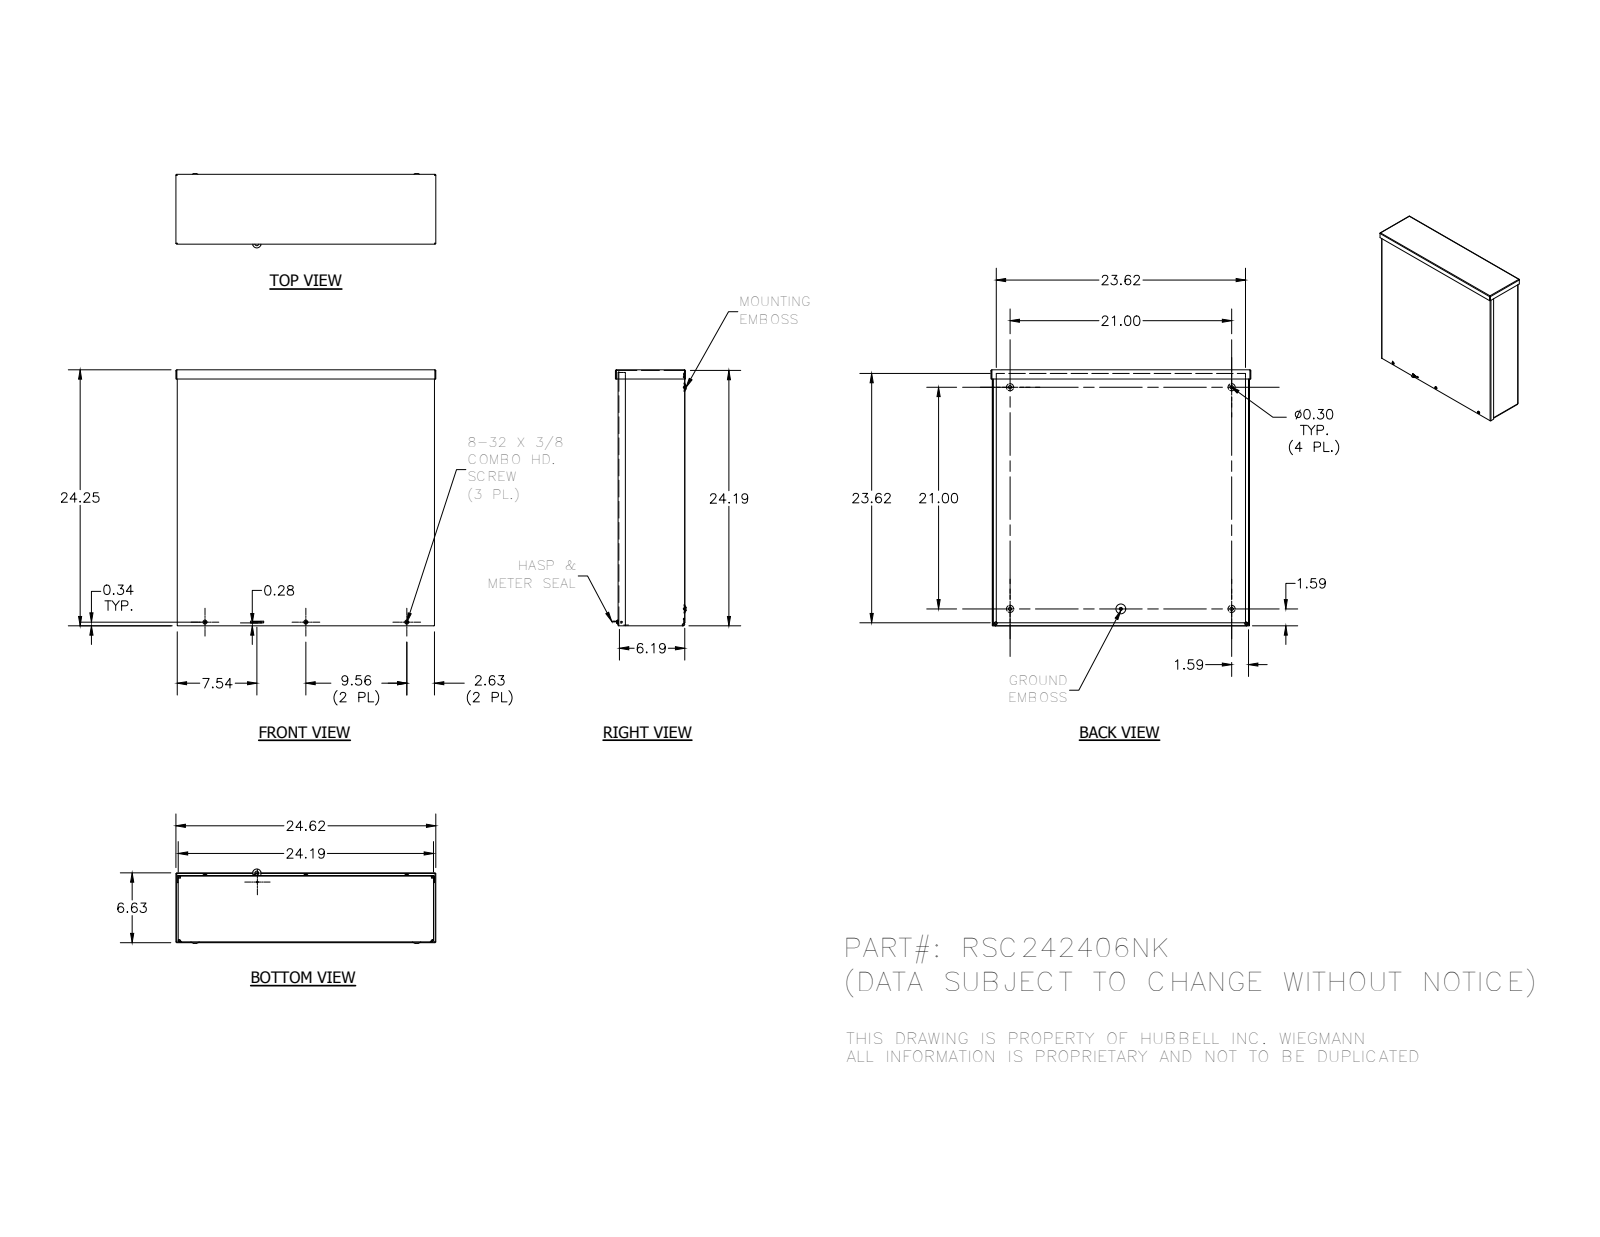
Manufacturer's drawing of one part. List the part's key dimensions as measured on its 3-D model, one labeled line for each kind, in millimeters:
Part name (STEP PRODUCT): RSC242406NK_WRAP; RSC2424NK_LID; RSC2406NK_CAP; 3183 (+3 more)
STEP written by: Autodesk Inventor 2014 (AUTOMOTIVE_DESIGN)
Units: millimetres
Bodies: 8 solids, 407 faces (173 planar, 83 cylindrical, 151 other)
Overall size (bounding box): 625.48 × 615.96 × 180.97
Volume: 2 158 000 mm³ · Surface area: 2 755 000 mm²
Round holes (diameter × count): ⌀7.95 ×6, ⌀7.62 ×4, ⌀3.76 ×3, ⌀3.17 ×1, ⌀3.45 ×1, ⌀3.96 ×1, ⌀4.19 ×1, ⌀9.52 ×1
Round bosses / shafts (diameter × count): ⌀9.75 ×3, ⌀4.17 ×3, ⌀5.8 ×1
Partial cylindrical surfaces — rounded edges, fillets, slot ends (radius × count): R0.79 ×8, R2.37 ×8, R3.17 ×8, R4.75 ×8, R1.4 ×4, R1.57 ×4, R2.38 ×4, R2.97 ×4
Main face-to-face distances: 1.58, 158.73, 157.15, 612.79, 1.59, 160.32, 158.74, 1.57, 614.37, 3.15
Hole centre spacings: 533.4, 640.01, 592.13, 242.88, 242.89, 266.7, 268.06, 268.59
